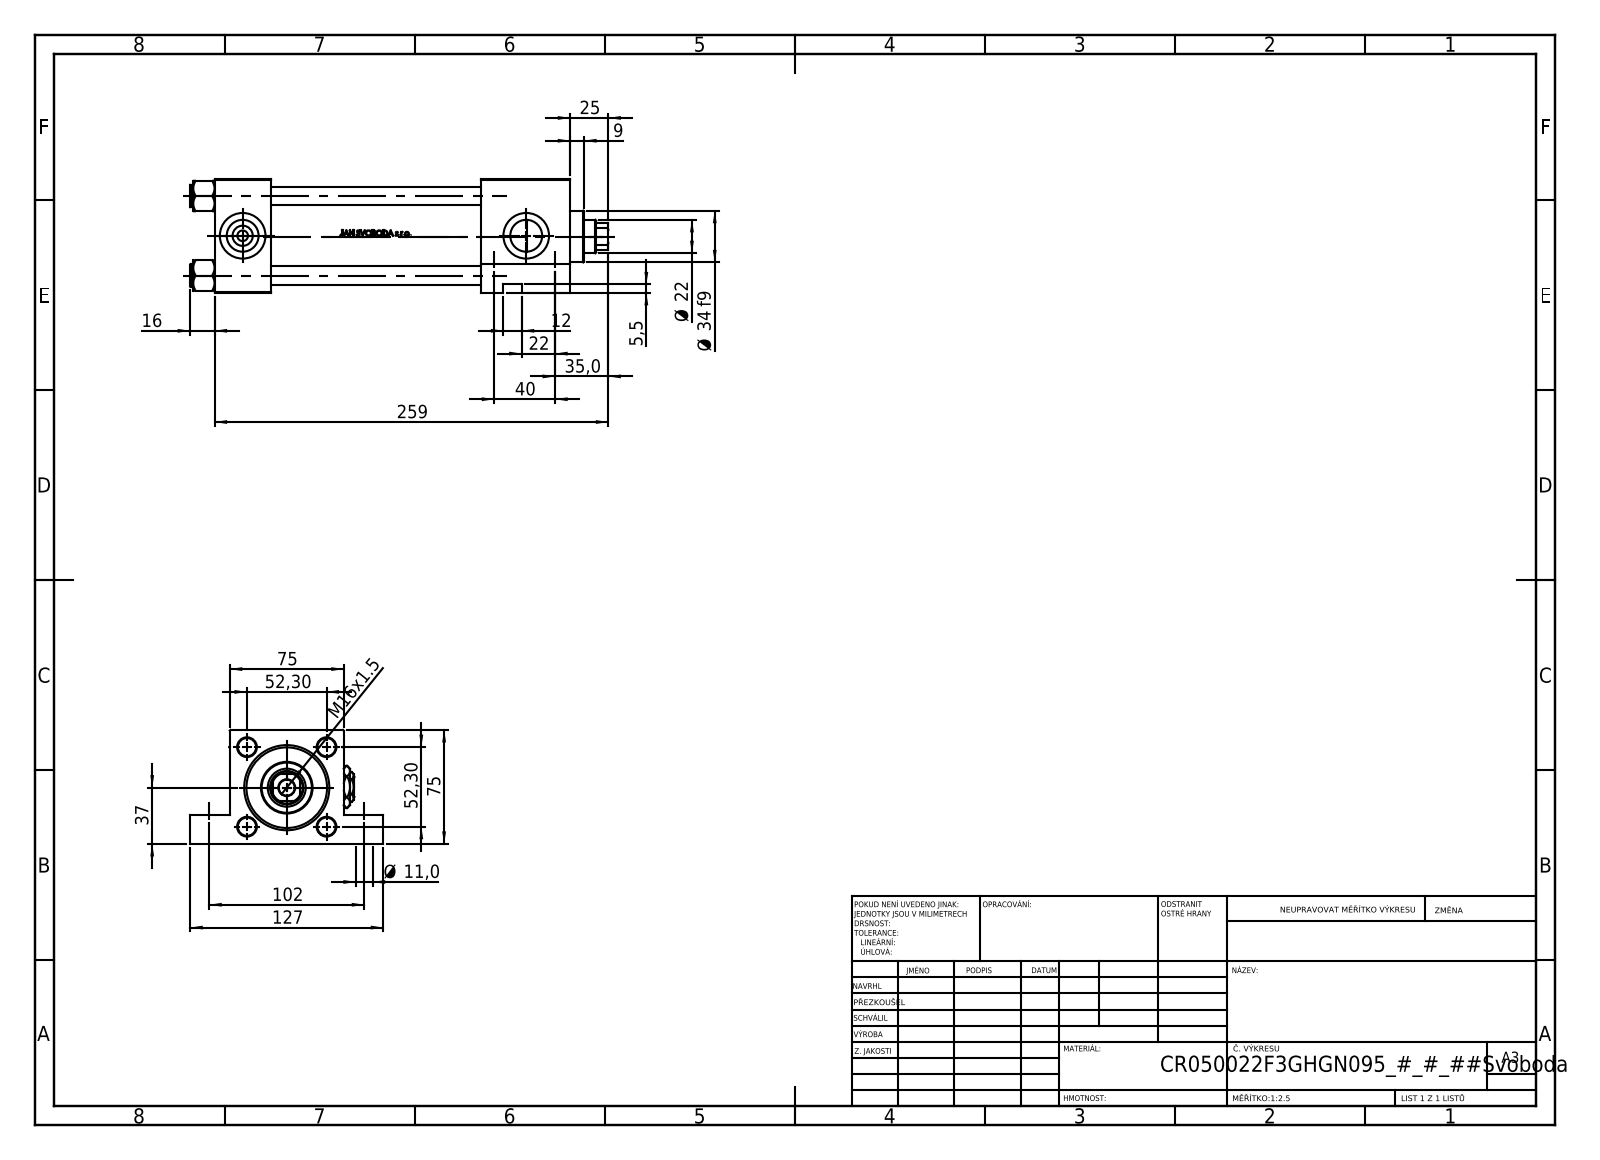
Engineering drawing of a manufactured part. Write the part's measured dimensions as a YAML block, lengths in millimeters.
part_name: "V215CR_F_Body; Zatka_pro_OIL_PORT; V215_VC_A; V215CR_VCP_F (+2 more)"
step_written_by: "SolidWorks 2019 (CONFIG_CONTROL_DESIGN)"
units: millimeters
bodies: {solids: 13, faces: 1199, planar: 483, cylindrical: 134, other: 582}
overall_size: [275, 127, 75]
volume: 808693
surface_area: 204840
round_holes:
  - {diameter: 11, count: 4}
  - {diameter: 12, count: 4}
  - {diameter: 20.96, count: 3}
  - {diameter: 30, count: 3}
  - {diameter: 7, count: 2}
  - {diameter: 10.5, count: 1}
  - {diameter: 17, count: 1}
  - {diameter: 22, count: 1}
  - {diameter: 25, count: 1}
  - {diameter: 41, count: 1}
  - {diameter: 50, count: 1}
  - {diameter: 53, count: 1}
round_bosses_or_shafts:
  - {diameter: 15, count: 4}
  - {diameter: 56, count: 1}
  - {diameter: 34, count: 1}
partial_cylinders:
  - {radius: 10.5, count: 1}
face_to_face_distances: [75, 37, 234, 197, 175, 138, 59, 19, 56, 205.3]
hole_center_spacings: [52.3, 36.63, 37.34, 40, 73.96, 102, 109.56, 13]
